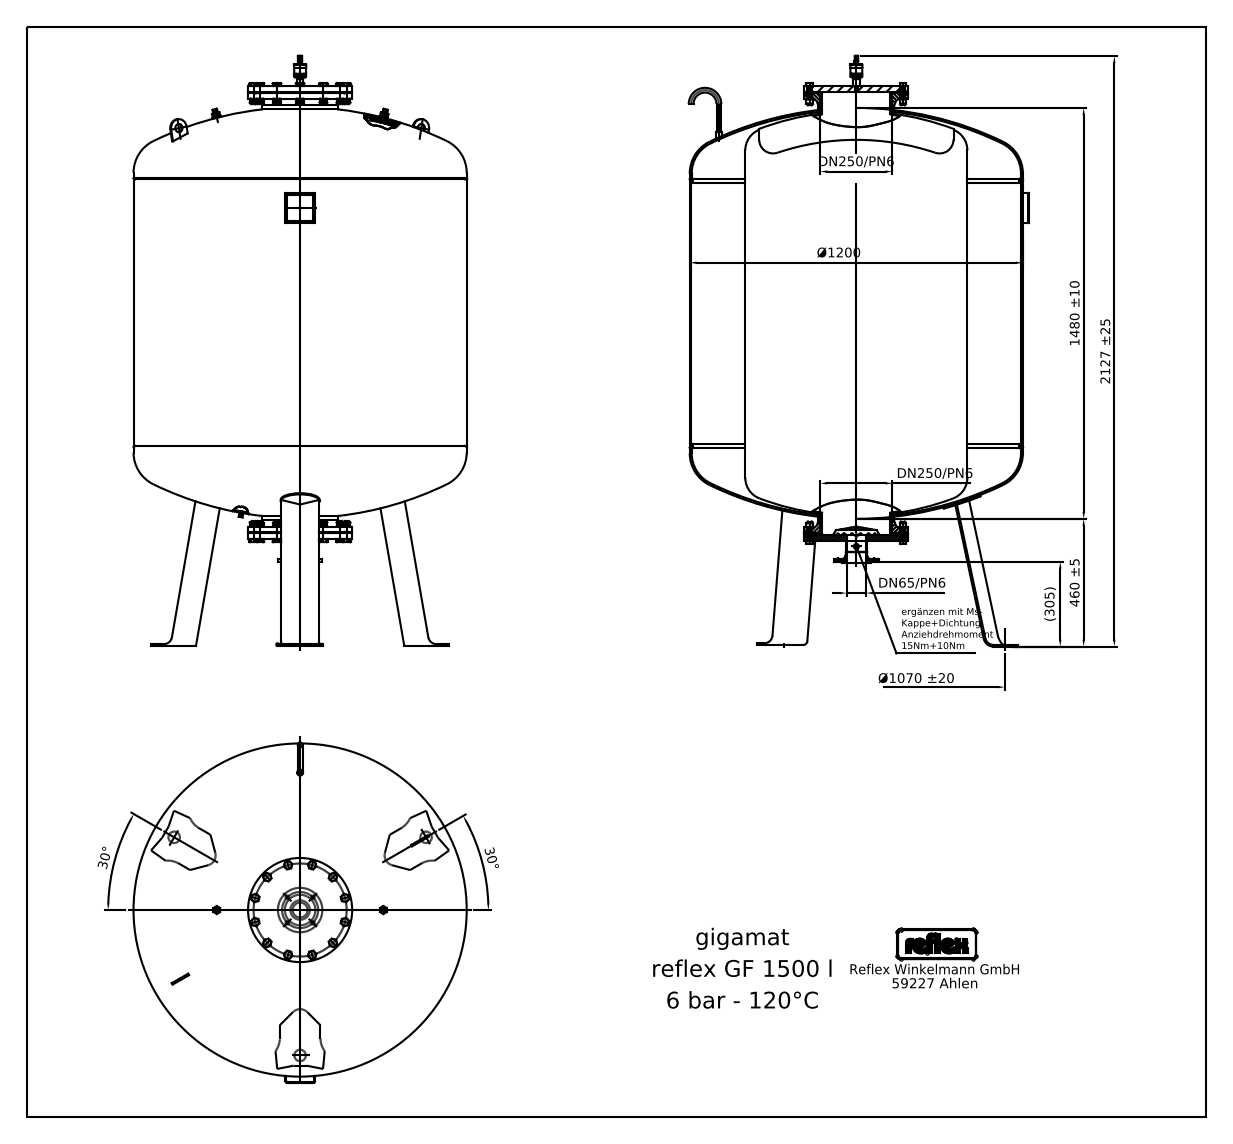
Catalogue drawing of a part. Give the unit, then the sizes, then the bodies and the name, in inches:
Units: inches
Overall size (bounding box): 83.74 × 47.244 × 47.244
Round holes (diameter × count): ⌀1.181 ×1, ⌀10.252 ×1
Round bosses / shafts (diameter × count): ⌀0.63 ×12, ⌀0.654 ×2, ⌀0.472 ×2, ⌀47.244 ×1, ⌀14.764 ×1, ⌀10.748 ×1, ⌀10.724 ×1, ⌀2.996 ×1
Partial cylindrical surfaces — rounded edges, fillets, slot ends (radius × count): R0.984 ×18, R0.332 ×4, R0.133 ×3, R0.354 ×3, R0.227 ×2, R0.398 ×2, R0.548 ×2, R0.555 ×2
Main face-to-face distances: 38.189, 0.866, 63.583, 1.063, 62.52, 50.512, 12.323, 51.378, 13.189, 13.071
Volume: 91 660 in³ · Surface area: 20 460 in²
Bodies: 20 solids, 863 faces (529 planar, 214 cylindrical, 120 other)
STEP written by: Mechanical Desktop 2008 (CONFIG_CONTROL_DESIGN)
